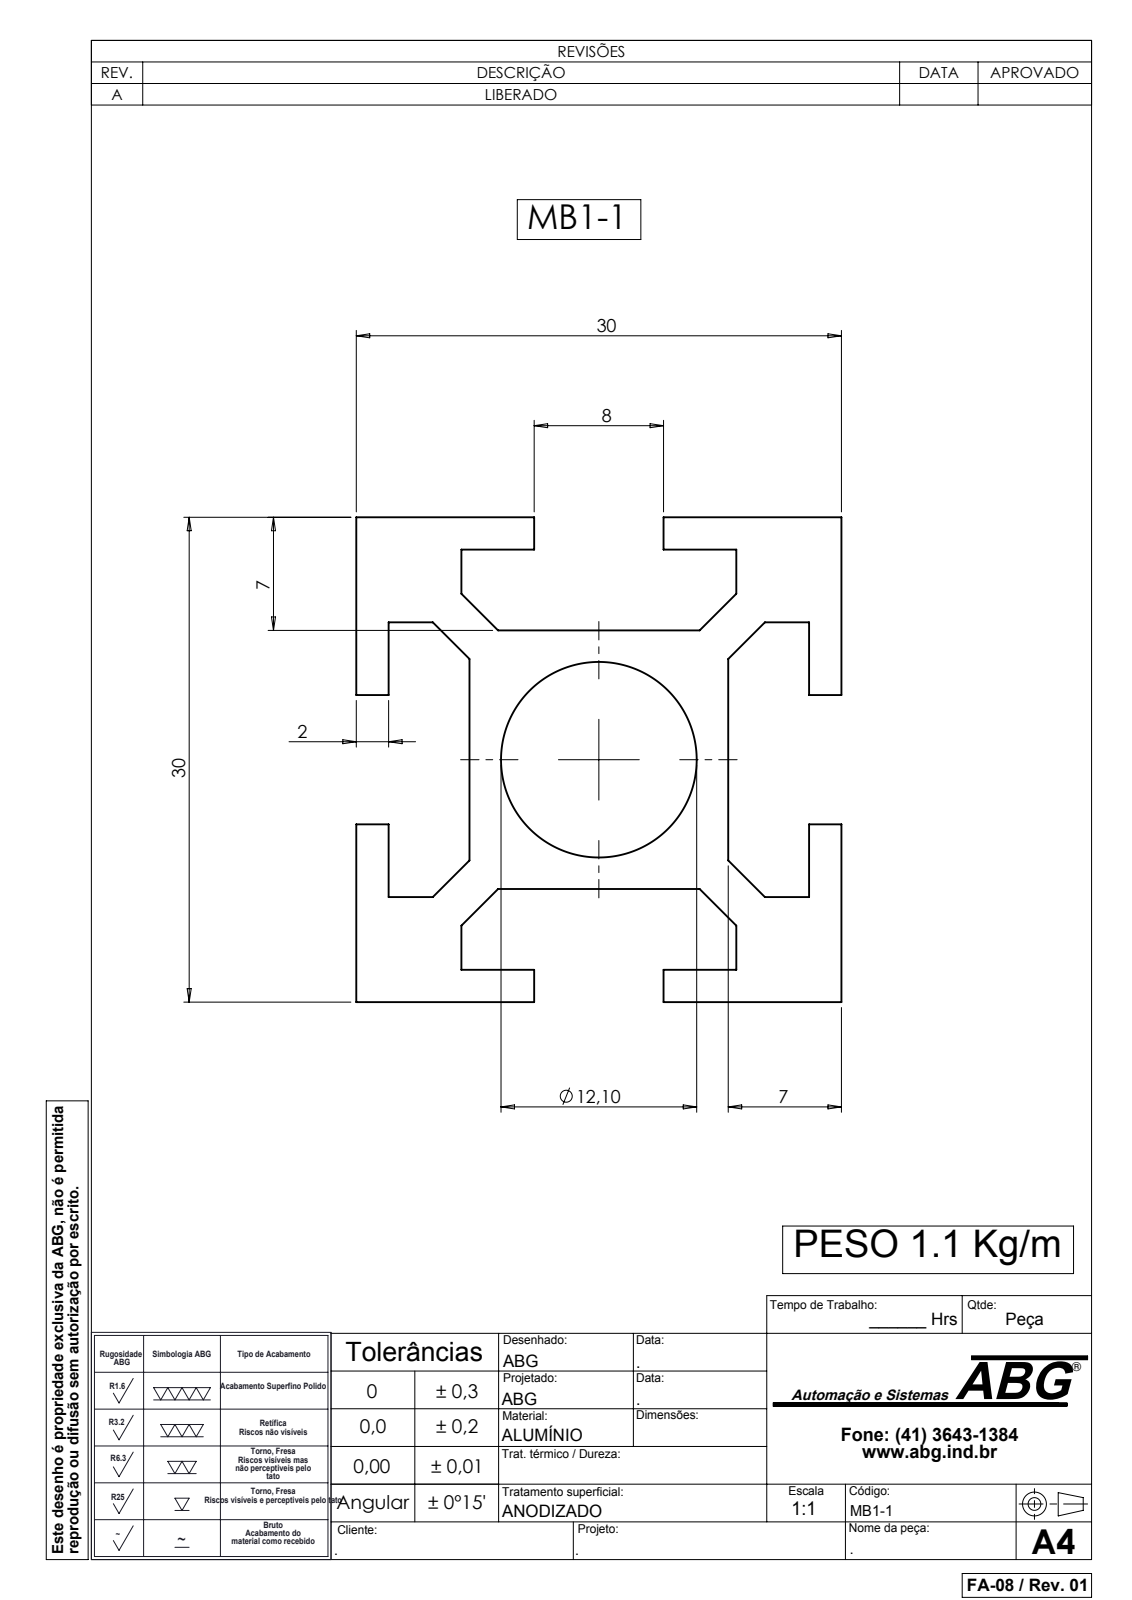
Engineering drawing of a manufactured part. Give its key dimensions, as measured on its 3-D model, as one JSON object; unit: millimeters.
{"part_name": "MB1-1", "step_written_by": "SolidWorks 2007 (CONFIG_CONTROL_DESIGN)", "units": "millimeters", "bodies": {"solids": 1, "faces": 48, "planar": 46, "cylindrical": 2, "other": 0}, "overall_size": [6000, 30, 30], "volume_mm3": 2409000, "surface_area_mm2": 1653000, "round_holes": [[12.1, 1]], "face_to_face_distances": [7, 23, 30, 4.5, 2, 28, 5, 21, 17, 16]}
